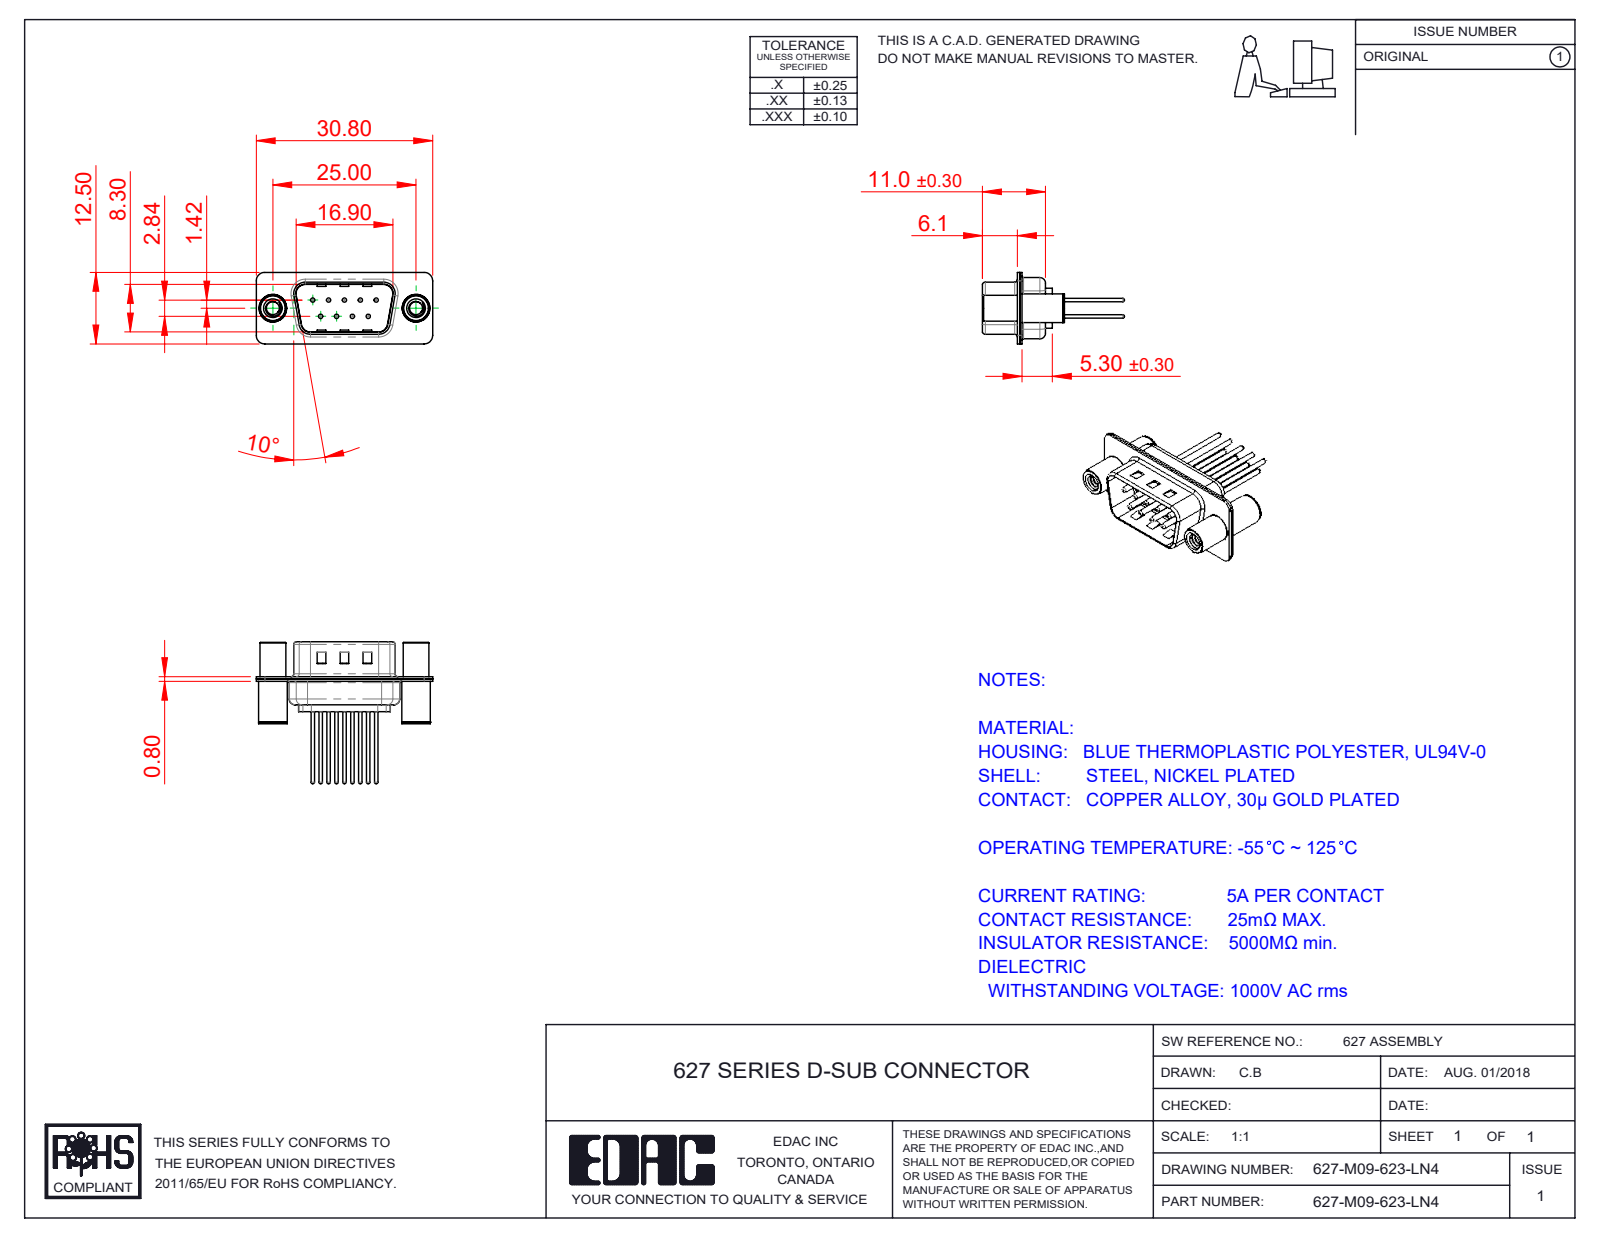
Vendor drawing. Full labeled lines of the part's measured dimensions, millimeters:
Part name (STEP PRODUCT): 627M 4-40 Threaded Standoff and Board Spacer; 627-M09-623-LN4; 627M Contact Row 1_23; 627M Shell Front_09 Contacts (+3 more)
STEP written by: SolidWorks 2020 (CONFIG_CONTROL_DESIGN)
Units: millimetres
Bodies: 14 solids, 723 faces (176 planar, 307 cylindrical, 240 other)
Overall size (bounding box): 30.8 × 24.77 × 12.5
Volume: 1 615 mm³ · Surface area: 4 220 mm²
Round holes (diameter × count): ⌀0.75 ×9, ⌀1.6 ×9, ⌀2 ×9, ⌀2.26 ×2, ⌀3.26 ×2, ⌀4 ×2, ⌀4.8 ×2
Round bosses / shafts (diameter × count): ⌀1.5 ×9, ⌀0.6 ×9, ⌀5 ×2, ⌀4.9 ×2, ⌀4.5 ×2
Partial cylindrical surfaces — rounded edges, fillets, slot ends (radius × count): R1.5 ×16, R2 ×12, R0.5 ×8, R1.6 ×8, R0.25 ×4, R0.6 ×4, R0.65 ×4, R0.9 ×4
Main face-to-face distances: 0.4, 0.8, 9.5, 9.1, 8.7, 0.65, 9.9, 1.2, 5.3, 6.1
Hole centre spacings: 3.16, 2.77, 5.54, 5.03, 5.04, 8.31, 7.1, 7.48
